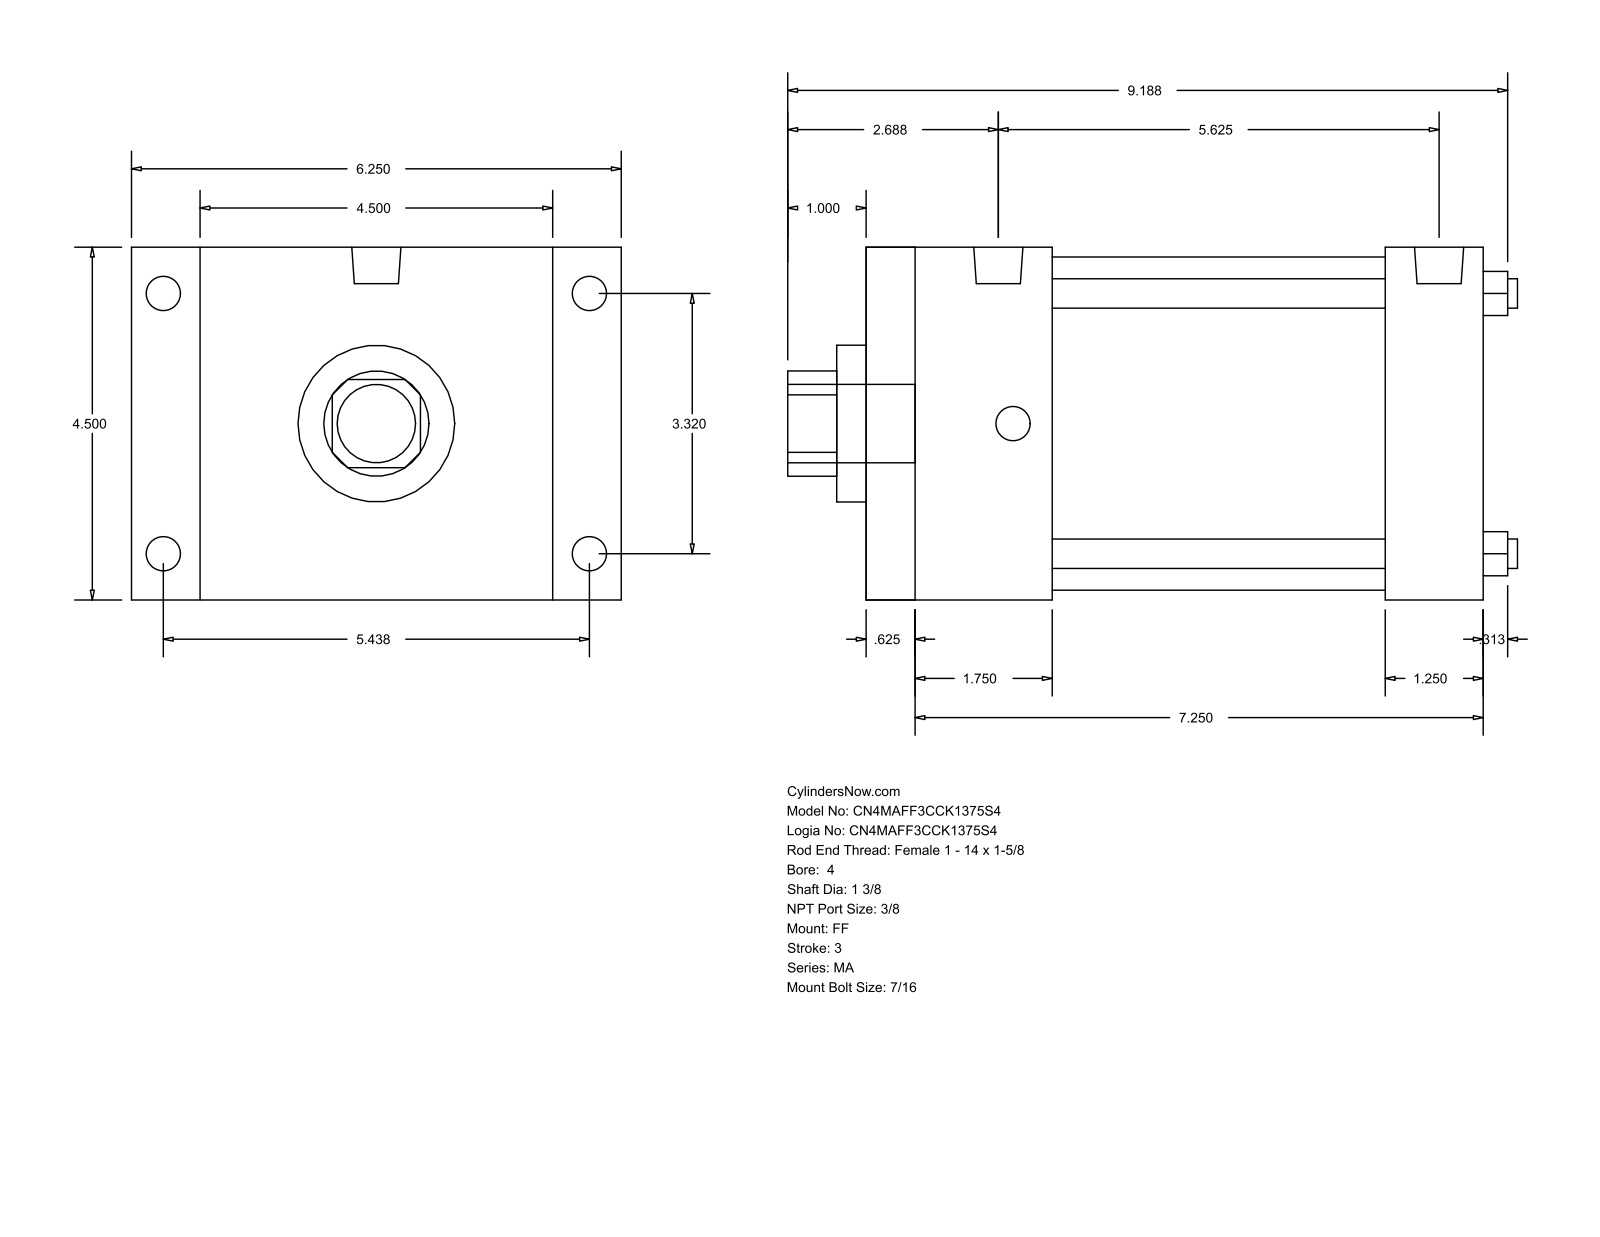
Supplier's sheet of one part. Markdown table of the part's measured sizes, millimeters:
| quantity | value |
| --- | --- |
| part name | MA_FF__0400_1.375 |
| STEP written by | GSSL Pune (CONFIG_CONTROL_DESIGN) |
| units | millimeters |
| bodies | 0 solids, 92 faces (64 planar, 28 cylindrical, 0 other) |
| overall size | 236.54 × 158.75 × 114.3 |
| round holes (diameter × count) | 9.53 × 4, 34.92 × 1, 50.8 × 1, 107.95 × 1 |
| round bosses / shafts (diameter × count) | 11.11 × 8, 15.93 × 2, 25.4 × 1 |
| partial cylindrical surfaces (radius × count) | 17.06 × 1 |
| main face-to-face distances | 114.3, 200.03, 15.87, 184.16, 22.23, 136.53, 168.28, 152.41, 31.75, 60.32 |
| hole center spacings | 59.62, 84.32, 119.25 |
